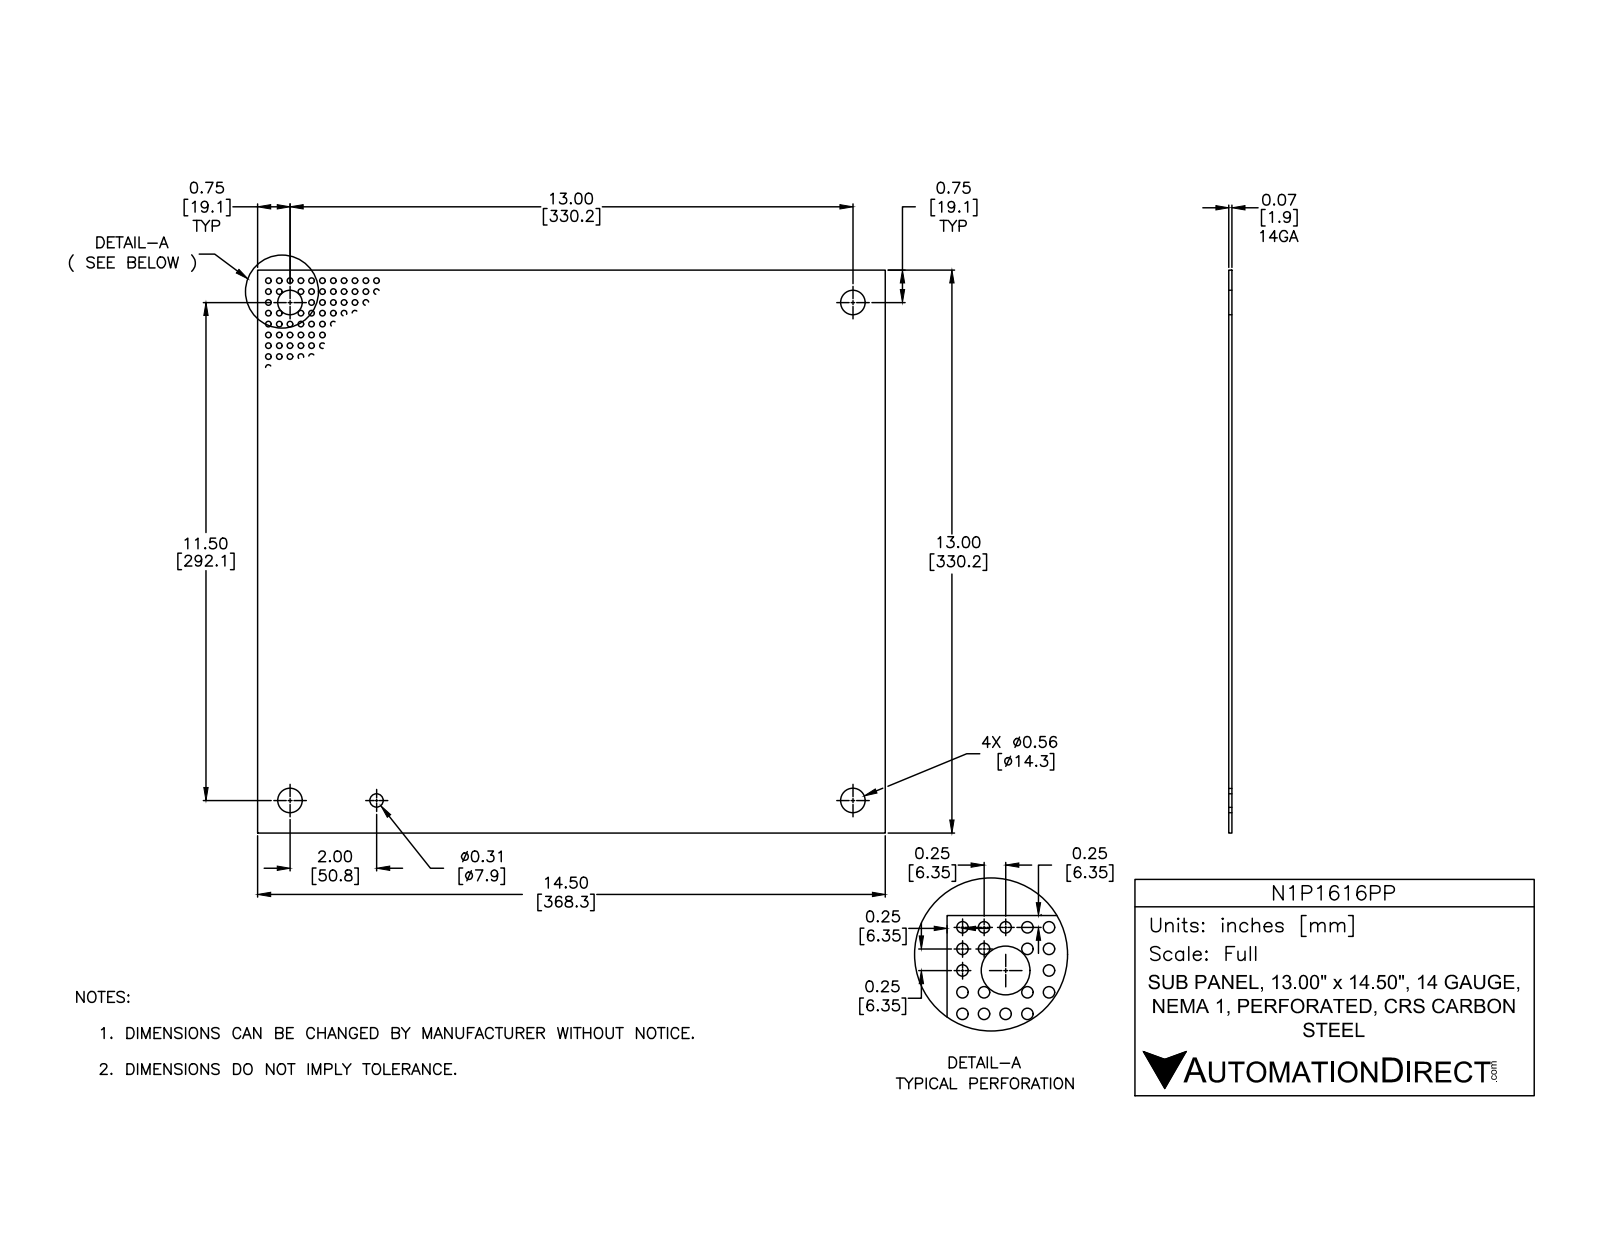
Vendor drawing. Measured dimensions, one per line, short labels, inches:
name: N1P_PP-LARGE
written by: Autodesk Inventor 2012 (AUTOMOTIVE_DESIGN)
unit: in
bodies: 1 solid, 11 faces (6 planar, 5 cylindrical, 0 other)
size: 14.5 × 13 × 0.074
volume: 13.87 in³; area: 379.5 in²
holes: 4× ⌀0.563, 1× ⌀0.312
face distances: 0.074, 13, 14.5
hole spacings: 11.5, 13, 17.357, 2, 11, 11.672, 15.914
